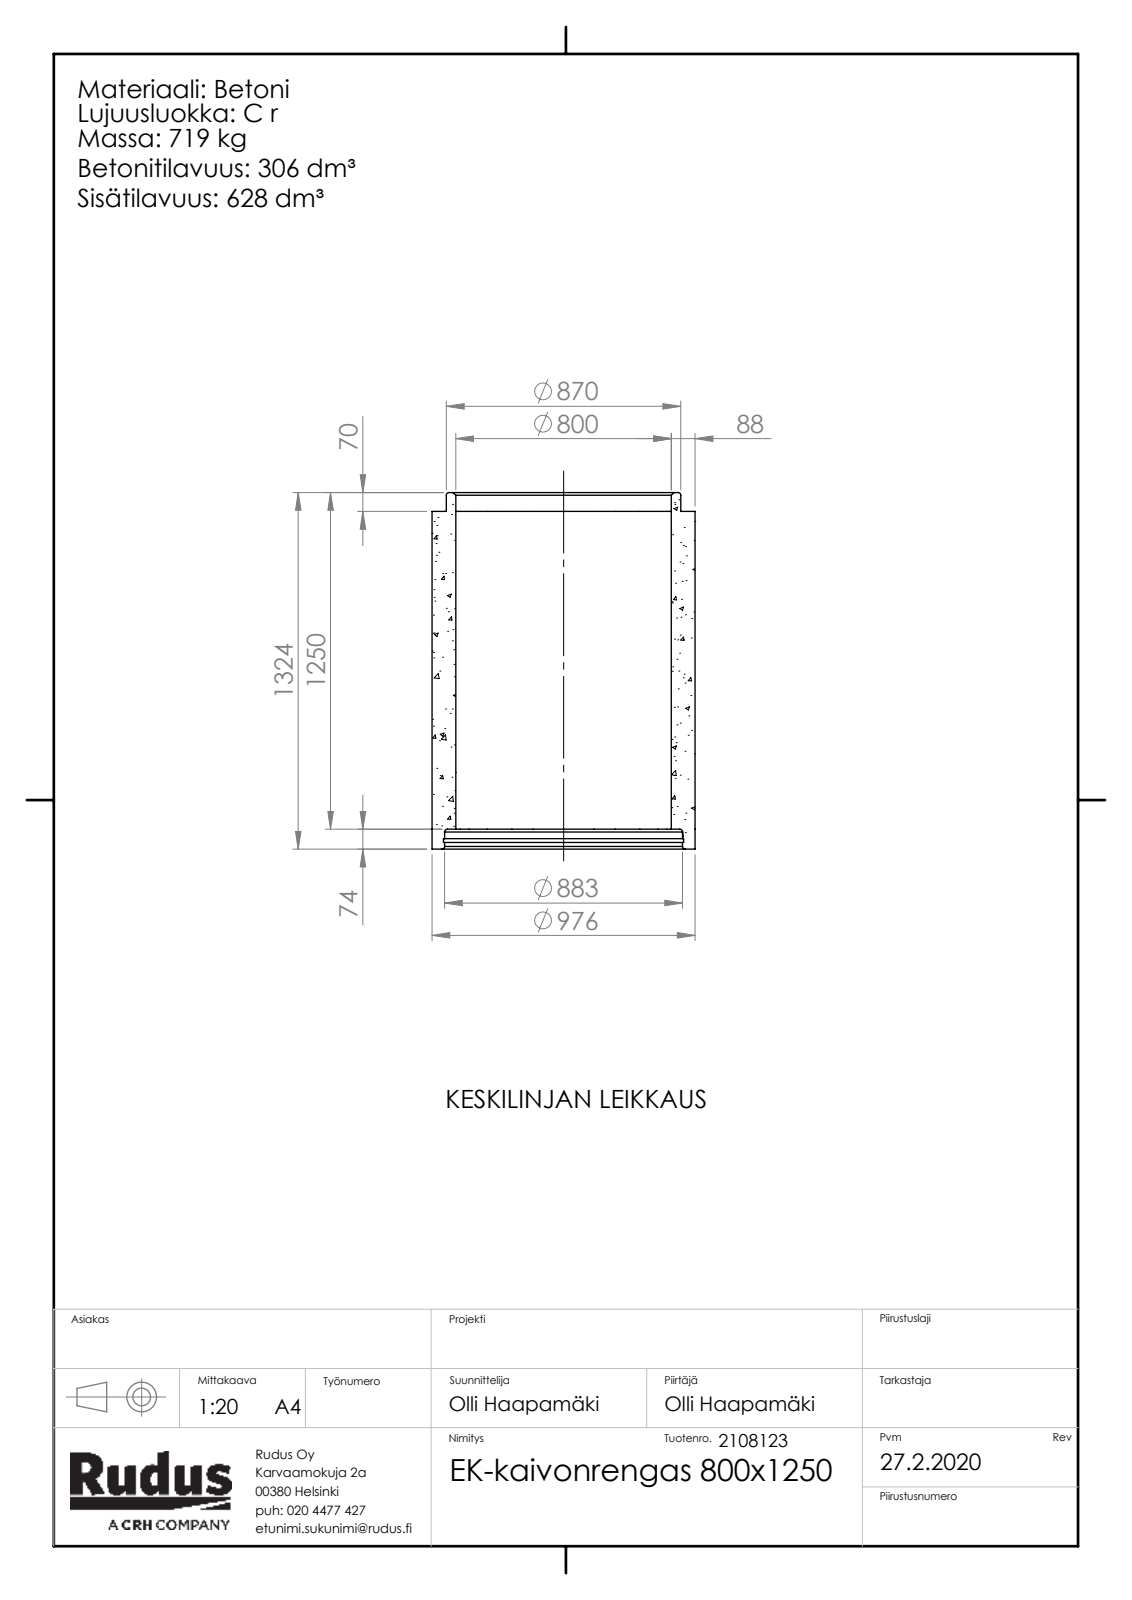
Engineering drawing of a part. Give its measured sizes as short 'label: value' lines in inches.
name: Rudus 2108123 EK-kaivonrengas 800x1250; EK-osa-kaivorunko_EK-kaivonrengas
written by: SolidWorks 2019 (CONFIG_CONTROL_DESIGN)
unit: in
bodies: 1 solid, 107 faces (7 planar, 12 cylindrical, 88 other)
size: 52.126 × 38.425 × 38.425
volume: 18 660 in³; area: 12 170 in²
holes: 1× ⌀31.496, 1× ⌀34.764, 1× ⌀35.079
bosses: 1× ⌀38.425, 1× ⌀34.252
face distances: 49.37, 2.913, 46.457, 52.126, 49.213, 2.756, 1.535, 1.378, 47.835, 50.591
